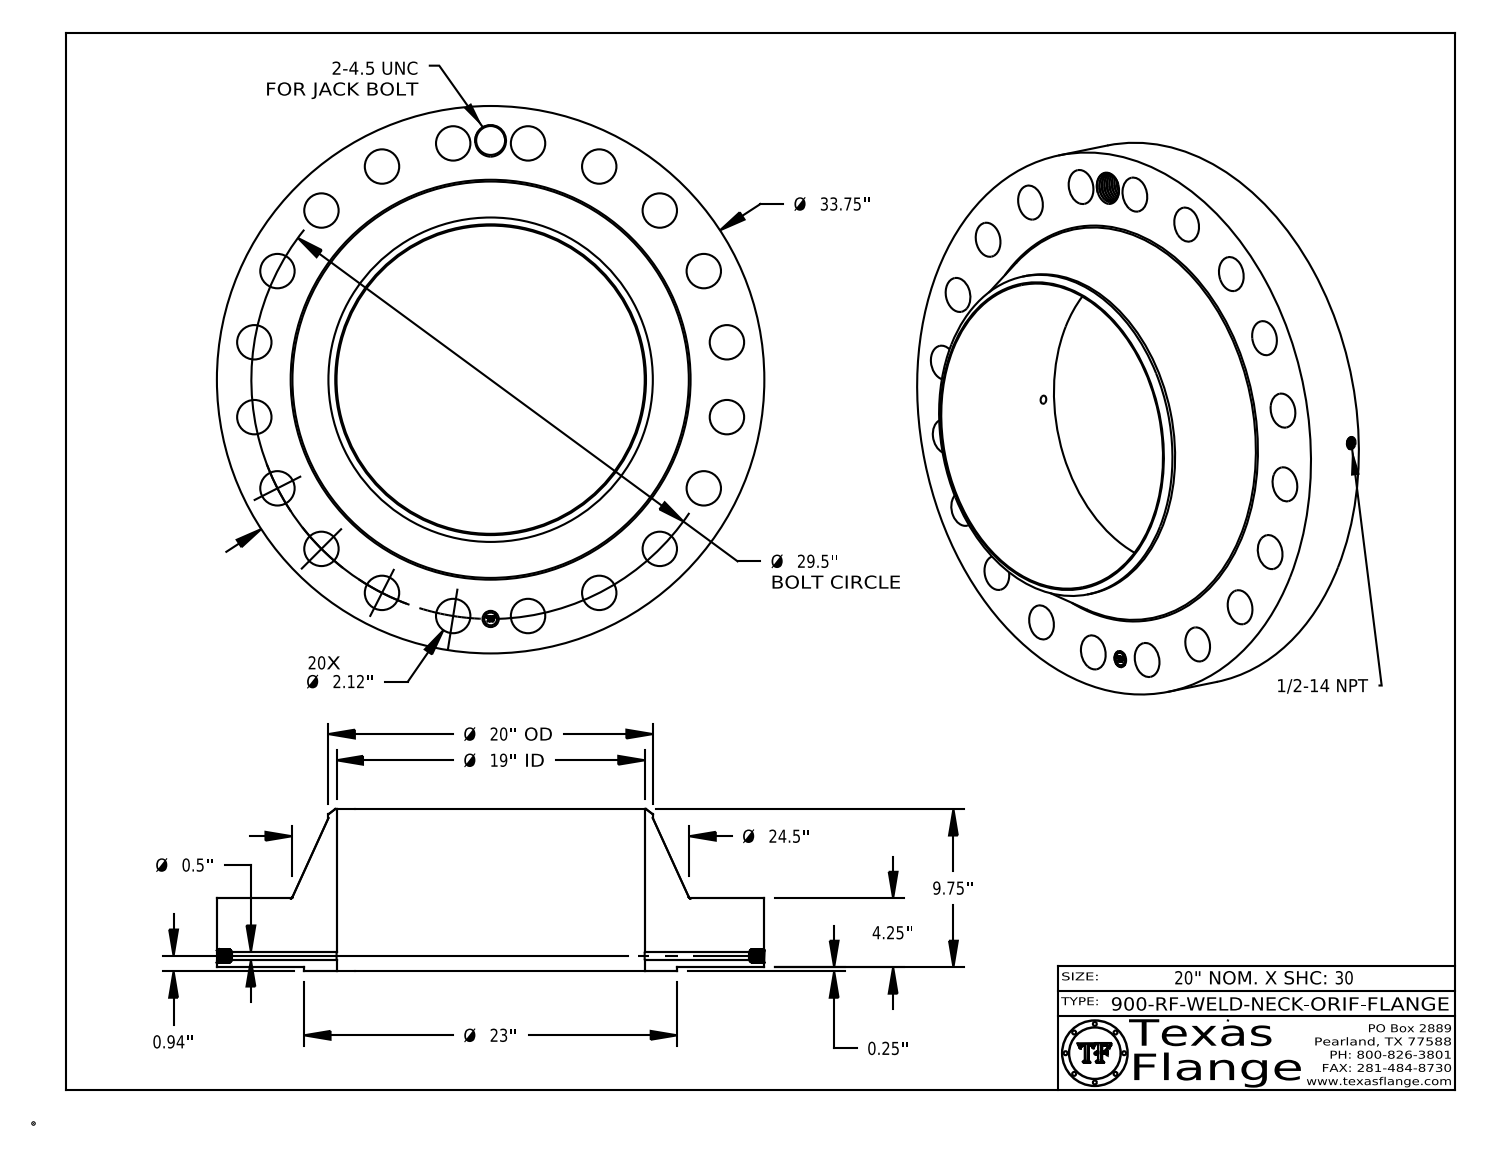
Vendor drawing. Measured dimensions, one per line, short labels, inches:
name: 900-RF-WELD-NECK
written by: CATIA V5 STEP AP214 (AUTOMOTIVE_DESIGN)
unit: in
bodies: 1 solid, 818 faces (369 planar, 126 cylindrical, 323 other)
size: 33.75 × 33.75 × 10
volume: 2 855 in³; area: 3 012 in²
holes: 20× ⌀2.12, 1× ⌀0.5, 1× ⌀0.672, 1× ⌀1, 1× ⌀1.781, 1× ⌀19
bosses: 8× ⌀0.061, 1× ⌀33.75, 1× ⌀23, 1× ⌀20, 1× ⌀0.788
face distances: 4.25, 0.25, 4.5, 10, 9.75, 5.5, 4.485, 4.235, 0.015, 5.515
hole spacings: 4.615, 9.116, 13.393, 17.34, 20.86, 23.866, 26.285, 29.137
